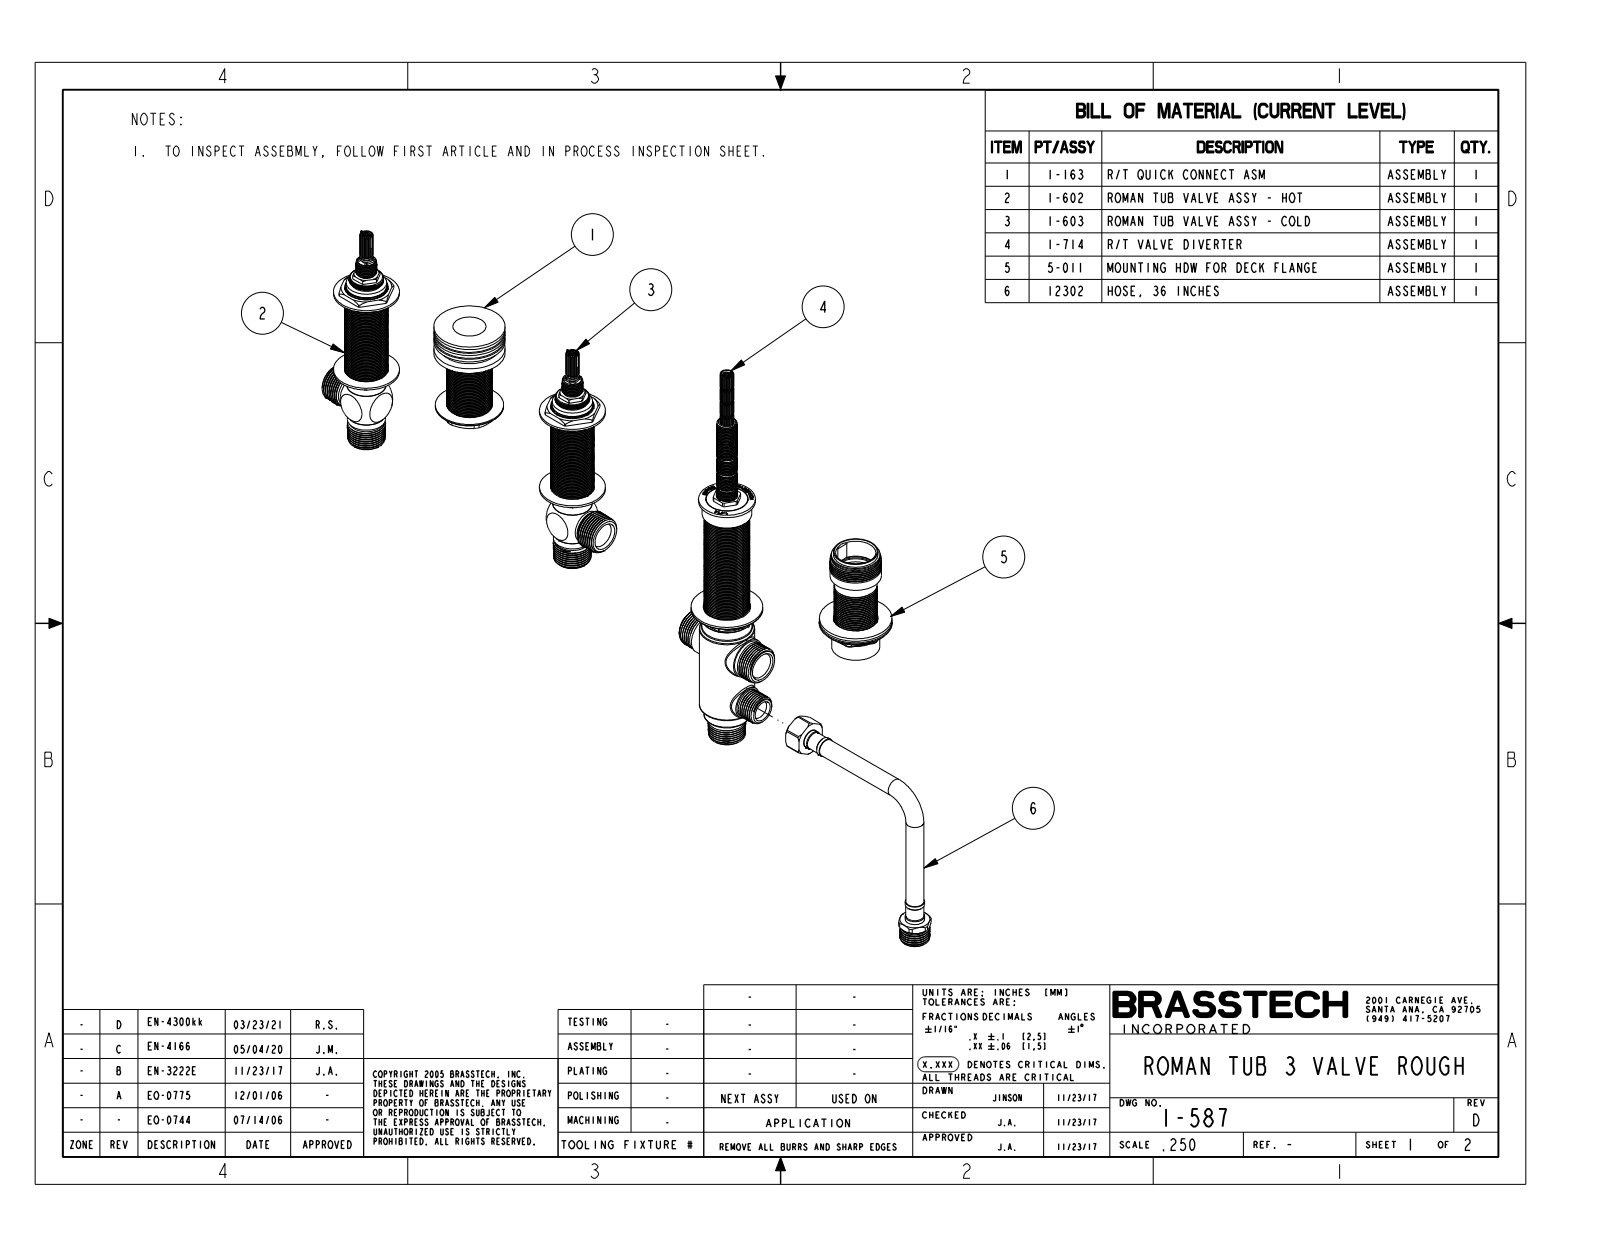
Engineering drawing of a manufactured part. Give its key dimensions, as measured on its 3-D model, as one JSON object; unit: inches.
{"part_name": "1-587", "step_written_by": "CREO PARAMETRIC BY PTC INC, 2018400 (AUTOMOTIVE_DESIGN)", "units": "inches", "bodies": {"solids": 7, "faces": 3884, "planar": 1049, "cylindrical": 1487, "other": 1348}, "overall_size": [21.415, 15.404, 2], "volume_in3": 33.35, "surface_area_in2": 291.8, "round_holes": [[0.196, 2], [0.201, 2], [0.236, 2], [0.276, 2], [0.138, 1], [0.202, 1], [0.274, 1], [0.393, 1], [0.394, 1], [0.417, 1], [0.48, 1], [0.52, 1]], "round_bosses_or_shafts": [[1.811, 2], [1.187, 2], [1.11, 2], [1.075, 2], [1.047, 2], [0.945, 2], [0.929, 2], [0.906, 2]], "partial_cylinders_radius": [[0.04, 14], [0.08, 8], [0.039, 6], [0.15, 6], [0.164, 3], [0.06, 2], [0.26, 2], [0.3, 2]], "face_to_face_distances": [0.061, 0.886, 0.04, 2.613, 2.573, 1.563, 2.448, 1.624, 0.825, 0.05], "hole_center_spacings": [0.703, 2.815, 5, 5.703, 6, 8, 11, 11.703]}
